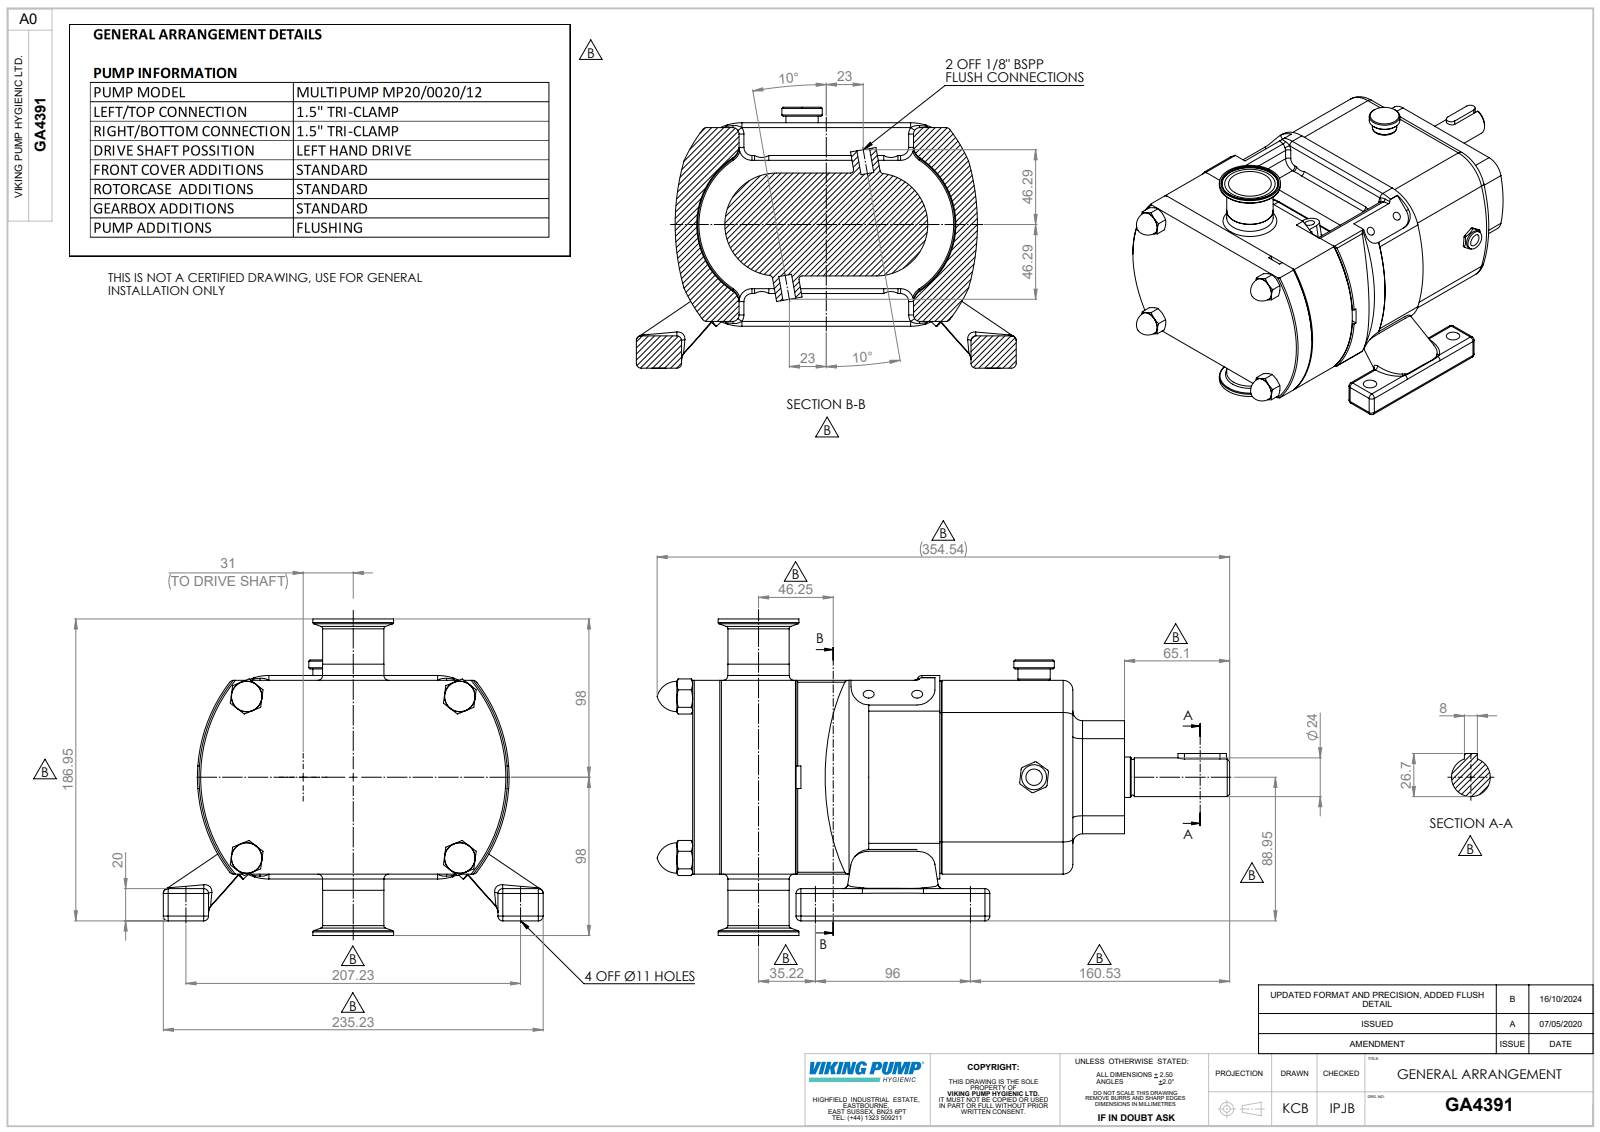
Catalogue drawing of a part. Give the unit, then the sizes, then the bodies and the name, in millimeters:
Units: millimetres
Overall size (bounding box): 354.54 × 235.23 × 196
Round holes (diameter × count): ⌀6.8 ×4, ⌀11 ×4, ⌀8 ×2, ⌀22.53 ×1, ⌀35 ×1
Round bosses / shafts (diameter × count): ⌀35 ×2, ⌀50 ×1, ⌀38 ×1, ⌀37.9 ×1, ⌀25.02 ×1, ⌀25 ×1, ⌀24 ×1, ⌀19.99 ×1
Partial cylindrical surfaces — rounded edges, fillets, slot ends (radius × count): R3 ×60, R2 ×18, R1 ×16, R6 ×8, R11.1 ×8, R1.27 ×6, R4 ×6, R8 ×6
Main face-to-face distances: 120, 109.04, 158.4, 267.44, 25, 95, 20.27, 99.73, 4.73, 74.73
Hole centre spacings: 30.05, 96, 109.44, 207.24, 61.08, 97, 125, 161.85
Volume: 4 758 000 mm³ · Surface area: 296 501 mm²
Bodies: 3 solids, 803 faces (239 planar, 277 cylindrical, 287 other)
Part name (STEP PRODUCT): Copy of CP20-0020-12 V L^GA4391; GA4391; Copy of Z94-5121-22 - 1.5 INCH^GA4391
STEP written by: SolidWorks 2023 (AUTOMOTIVE_DESIGN)
